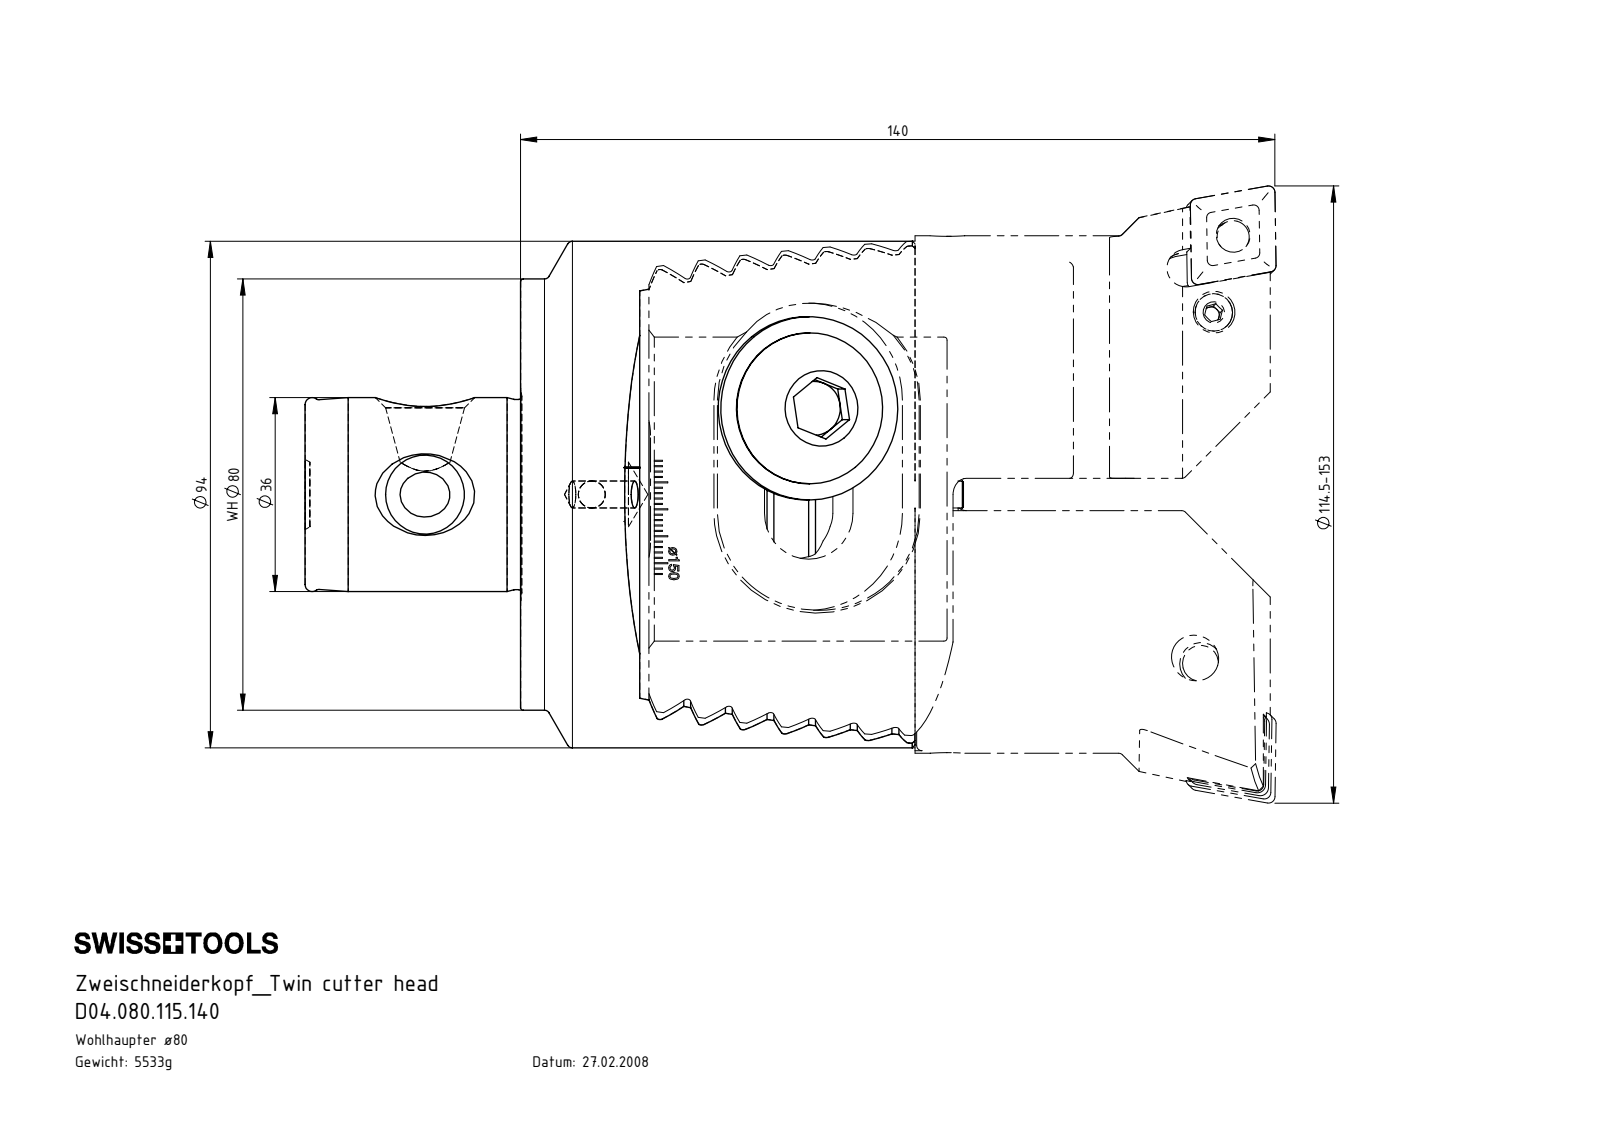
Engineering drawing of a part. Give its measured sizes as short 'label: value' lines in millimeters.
name: WCE-ER2.101.004_A; CNMG160612; Z72-ER3.001.030; Z94-WCE.101.067 (+8 more)
written by: SolidWorks 2015 (AUTOMOTIVE_DESIGN)
unit: mm
bodies: 20 solids, 1258 faces (663 planar, 255 cylindrical, 340 other)
size: 180.22 × 114.5 × 94
volume: 703 152 mm³; area: 127 384 mm²
holes: 3× ⌀4.2, 2× ⌀2, 2× ⌀6.35, 2× ⌀7, 2× ⌀8.05, 2× ⌀8.4, 2× ⌀14, 2× ⌀17, 2× ⌀17.5, 1× ⌀3.3, 1× ⌀5, 1× ⌀12
bosses: 3× ⌀6, 2× ⌀34, 2× ⌀28, 2× ⌀16, 2× ⌀8, 2× ⌀7.9, 2× ⌀6.4, 2× ⌀4
rounds: 16× R1, 14× R0.58, 12× R0.58, 8× R1.2, 8× R1.5, 6× R3, 6× R3.5, 4× R0.3
face distances: 6.93, 13.86, 27.71, 20.78, 13.85, 20.79, 6.9, 13.19, 34.64, 7
hole spacings: 14.76, 15.01, 25, 48.3
